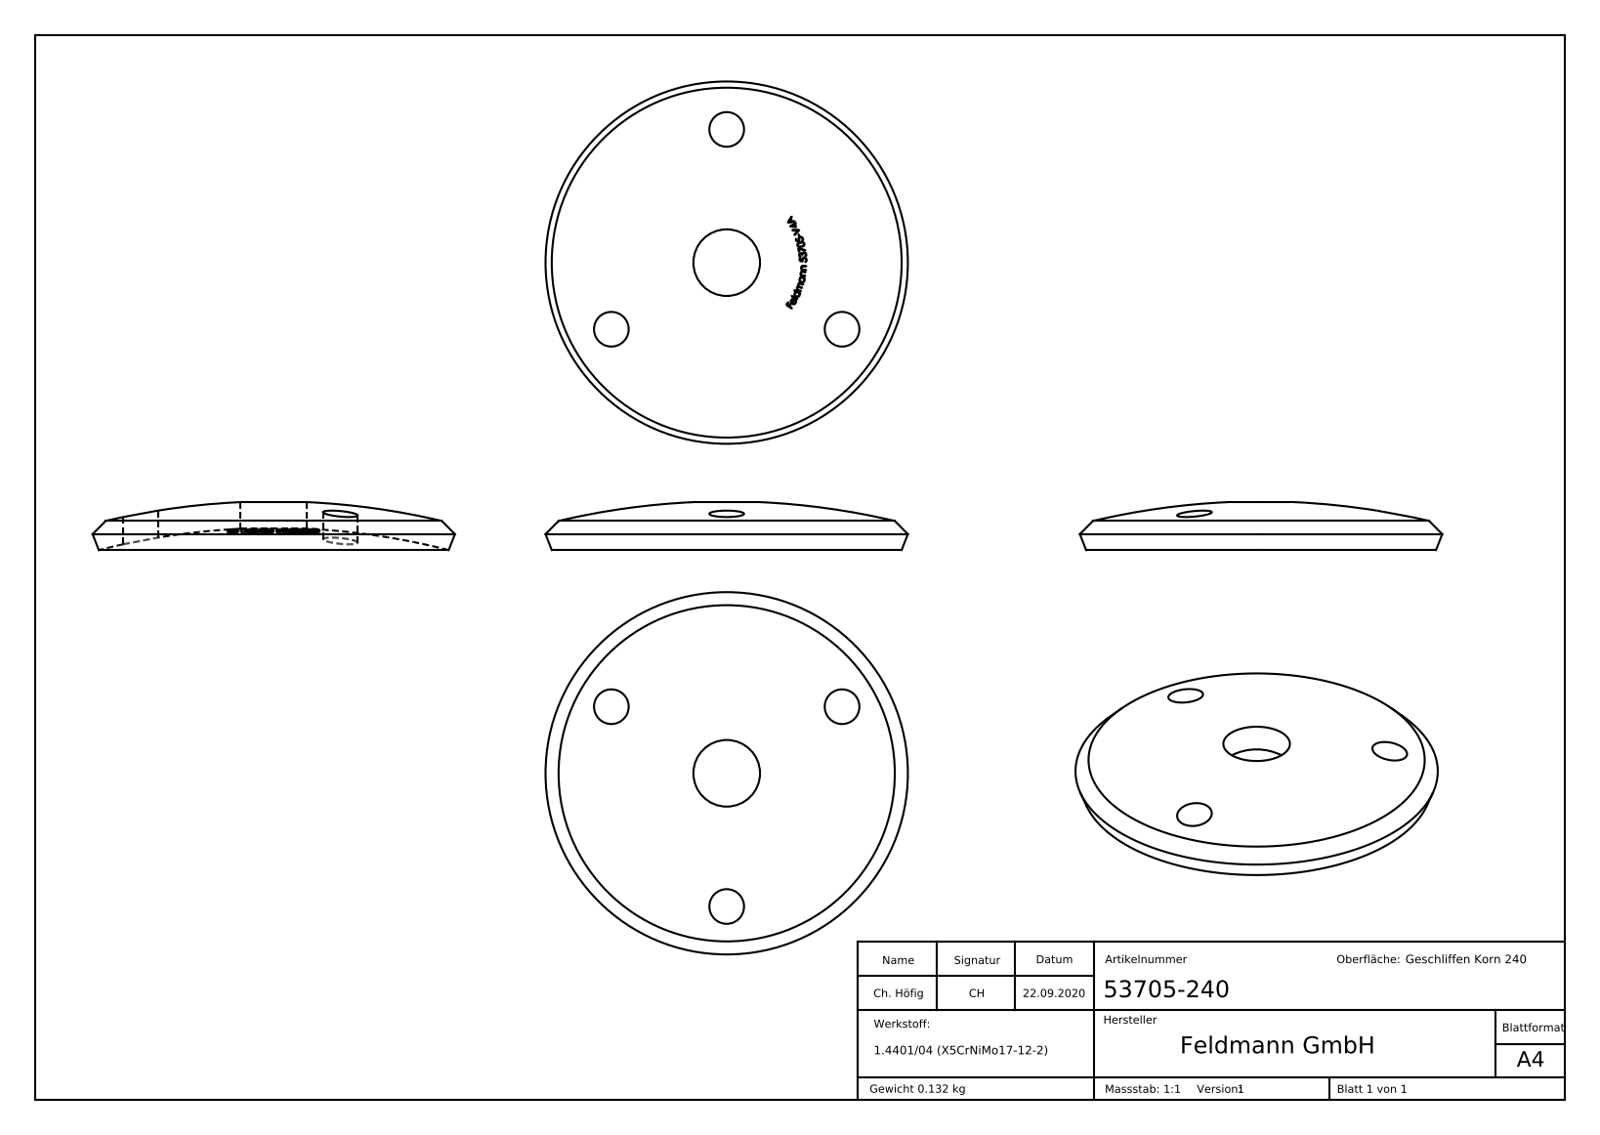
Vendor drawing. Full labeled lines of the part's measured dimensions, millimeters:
Part name (STEP PRODUCT): 53705-V4A
STEP written by: SolidWorks 2018 (CONFIG_CONTROL_DESIGN)
Units: millimetres
Bodies: 1 solid, 236 faces (110 planar, 8 cylindrical, 118 other)
Overall size (bounding box): 68 × 68 × 9
Volume: 16 448 mm³ · Surface area: 8 109 mm²
Round holes (diameter × count): ⌀6.5 ×3, ⌀12.5 ×1
Main face-to-face distances: 0.66, 0.54, 0.85, 1.32, 0.79, 0.53, 0.73, 1.45, 0.41, 0.67
Hole centre spacings: 25, 43.3
